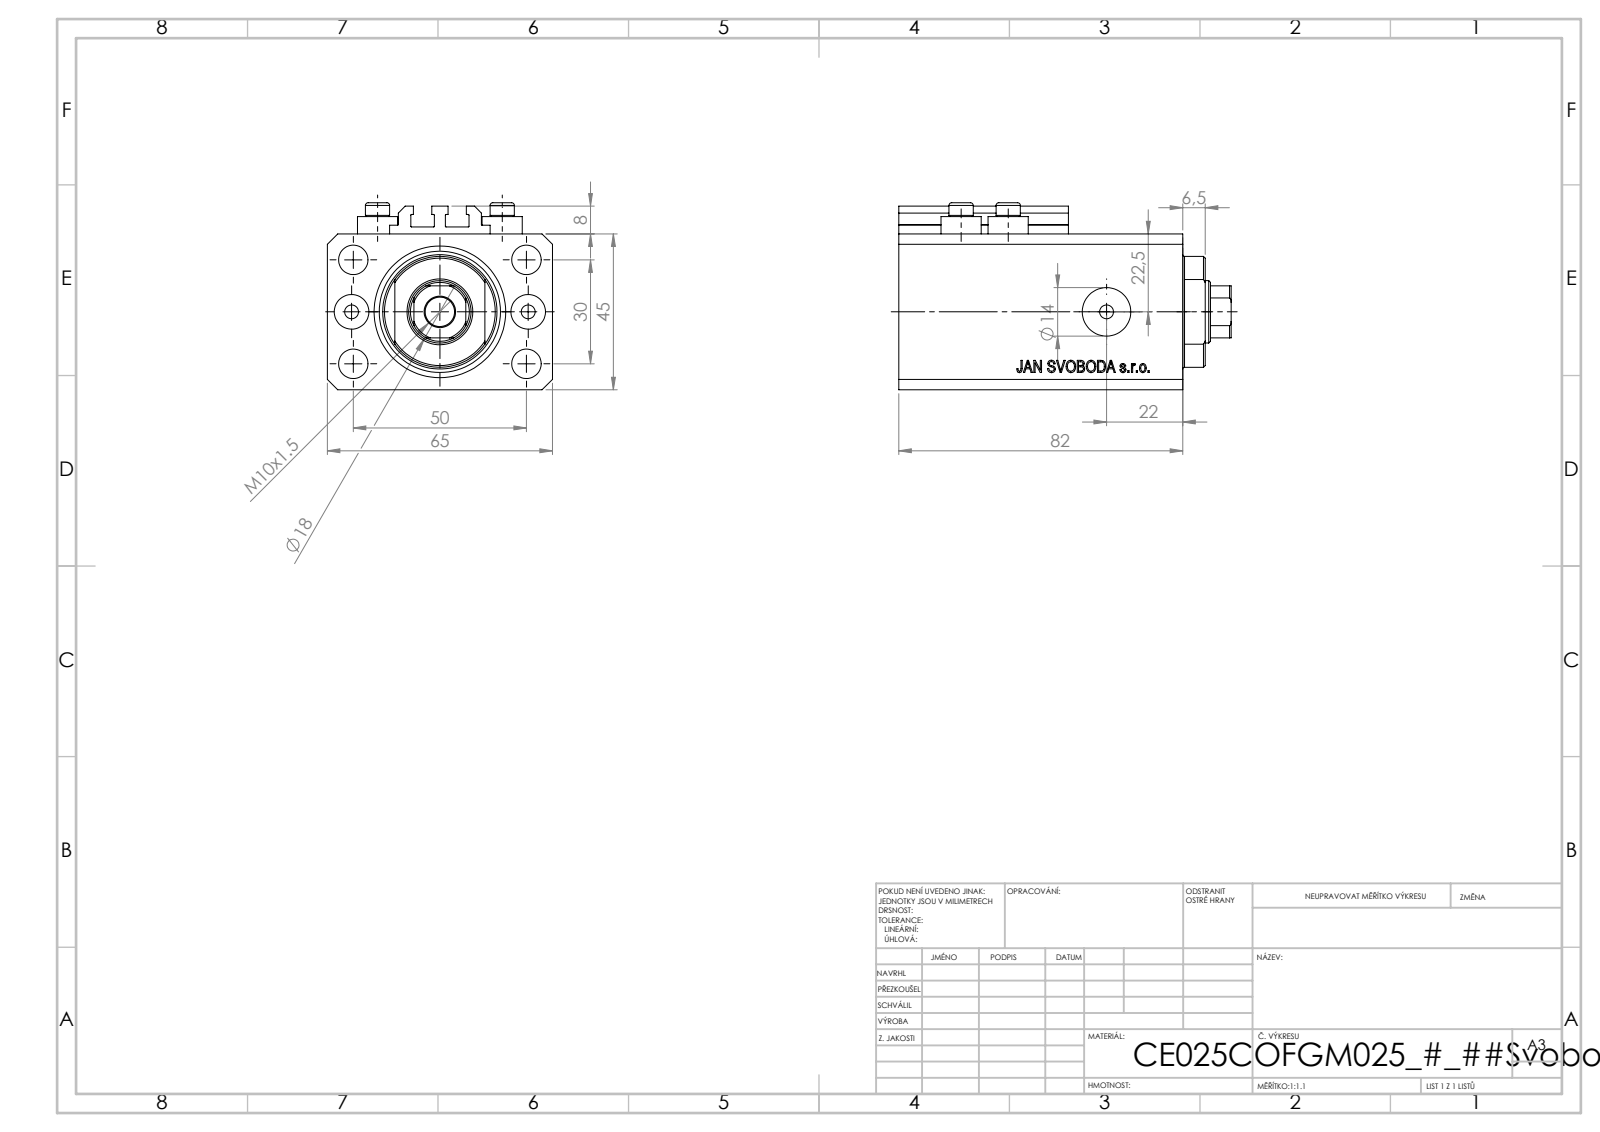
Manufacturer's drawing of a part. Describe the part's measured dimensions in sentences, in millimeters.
The part is named "V250CE_VC_C; V250CE_C_VCP; ALLEN BOLT V250CE; V250CE_C_Body". Its 3-D file was written by "SolidWorks 2019 (CONFIG_CONTROL_DESIGN)". It is 8 solids with 1034 faces: 504 planar, 86 cylindrical and 444 other. Overall it measures 96 by 65 by 54 millimeters. Its volume is 224 788 cubic millimeters and its surface area 60 044 square millimeters. Round holes: 8 of diameter 4, 5 of diameter 8.5, 2 of diameter 10, 2 of diameter 14, 1 of diameter 18, 1 of diameter 25, 1 of diameter 38. Round bosses or shafts: 4 of diameter 11.6, 4 of diameter 7. Partial cylindrical surfaces (rounded edges, fillets, slot ends): 10 of radius 0.2, 1 of radius 8.5, 1 of radius 16. The main face-to-face distances are 45, 65, 14, 68, 82, 47, 6.9, 61.1, 75.1, 3. The hole center spacings are 15.01, 29.15, 52.68, 13.6, 25.5, 30, 36, 38.48.
